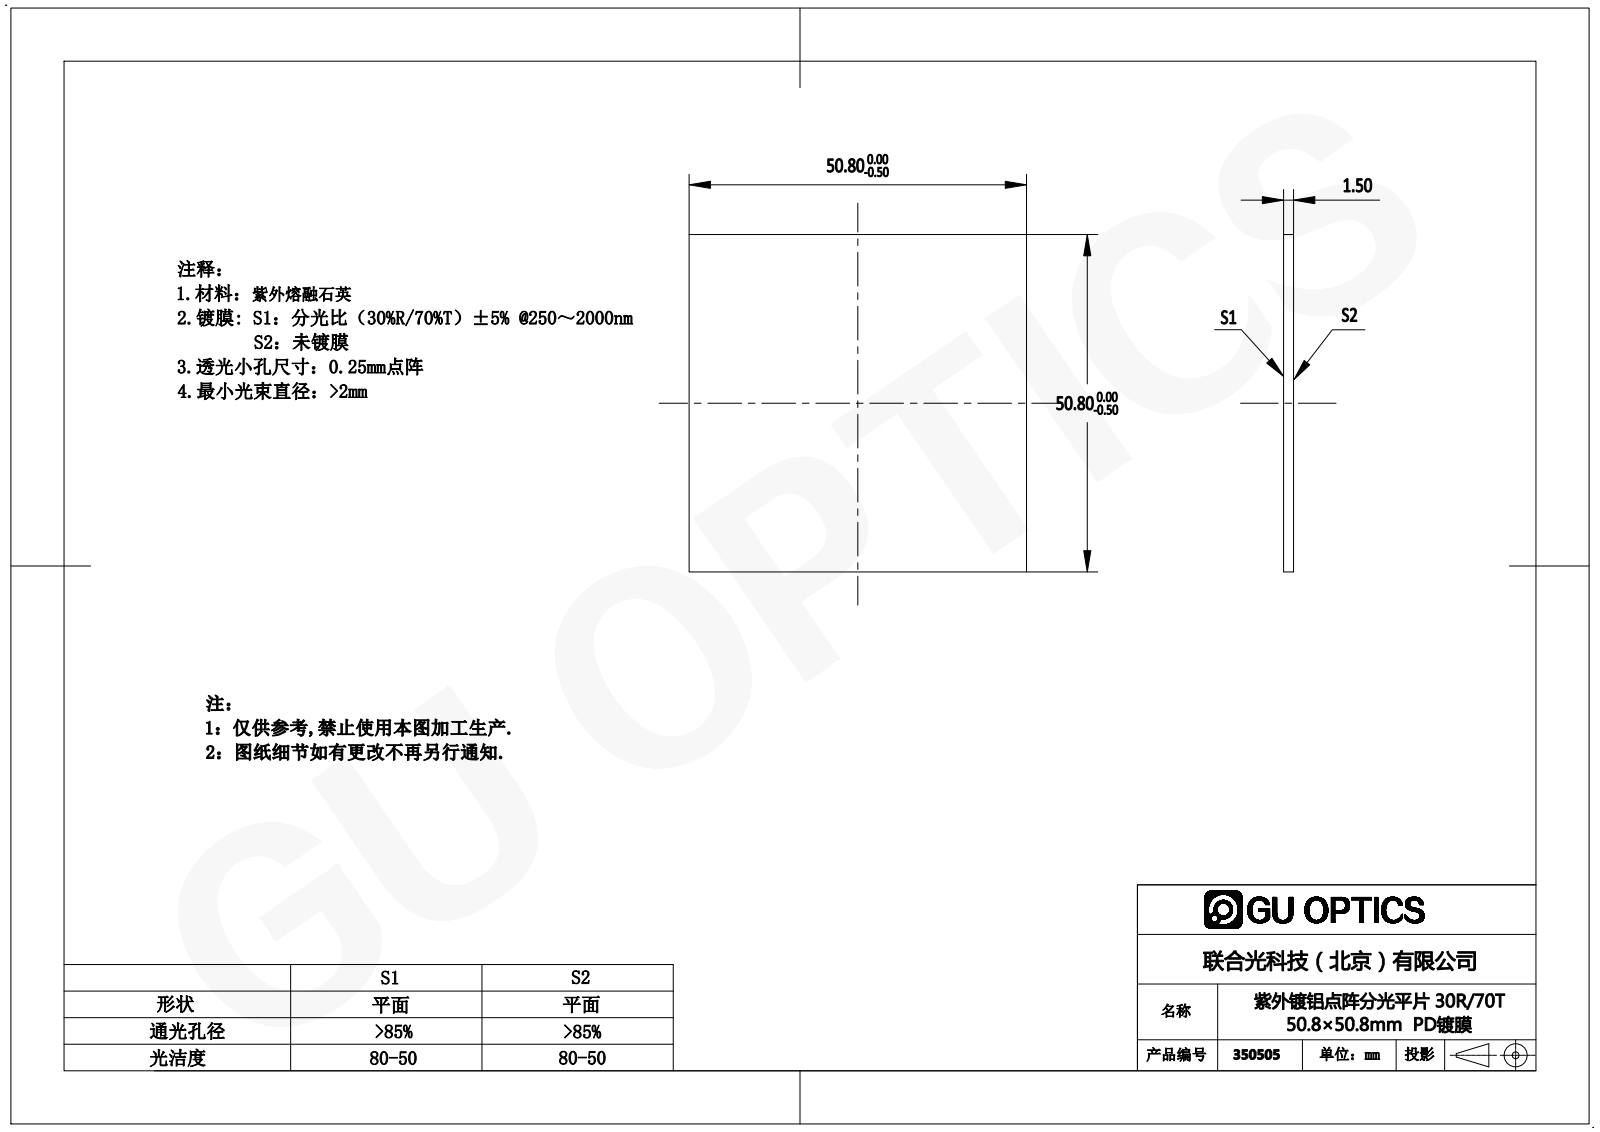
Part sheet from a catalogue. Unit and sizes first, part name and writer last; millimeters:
Units: millimetres
Overall size (bounding box): 50.8 × 50.8 × 1.5
Main face-to-face distances: 1.5, 50.8
Volume: 3 871 mm³ · Surface area: 5 466 mm²
Bodies: 1 solid, 6 faces (6 planar, 0 cylindrical, 0 other)
Part name (STEP PRODUCT): 350505
STEP written by: SolidWorks 2016 (AUTOMOTIVE_DESIGN)
